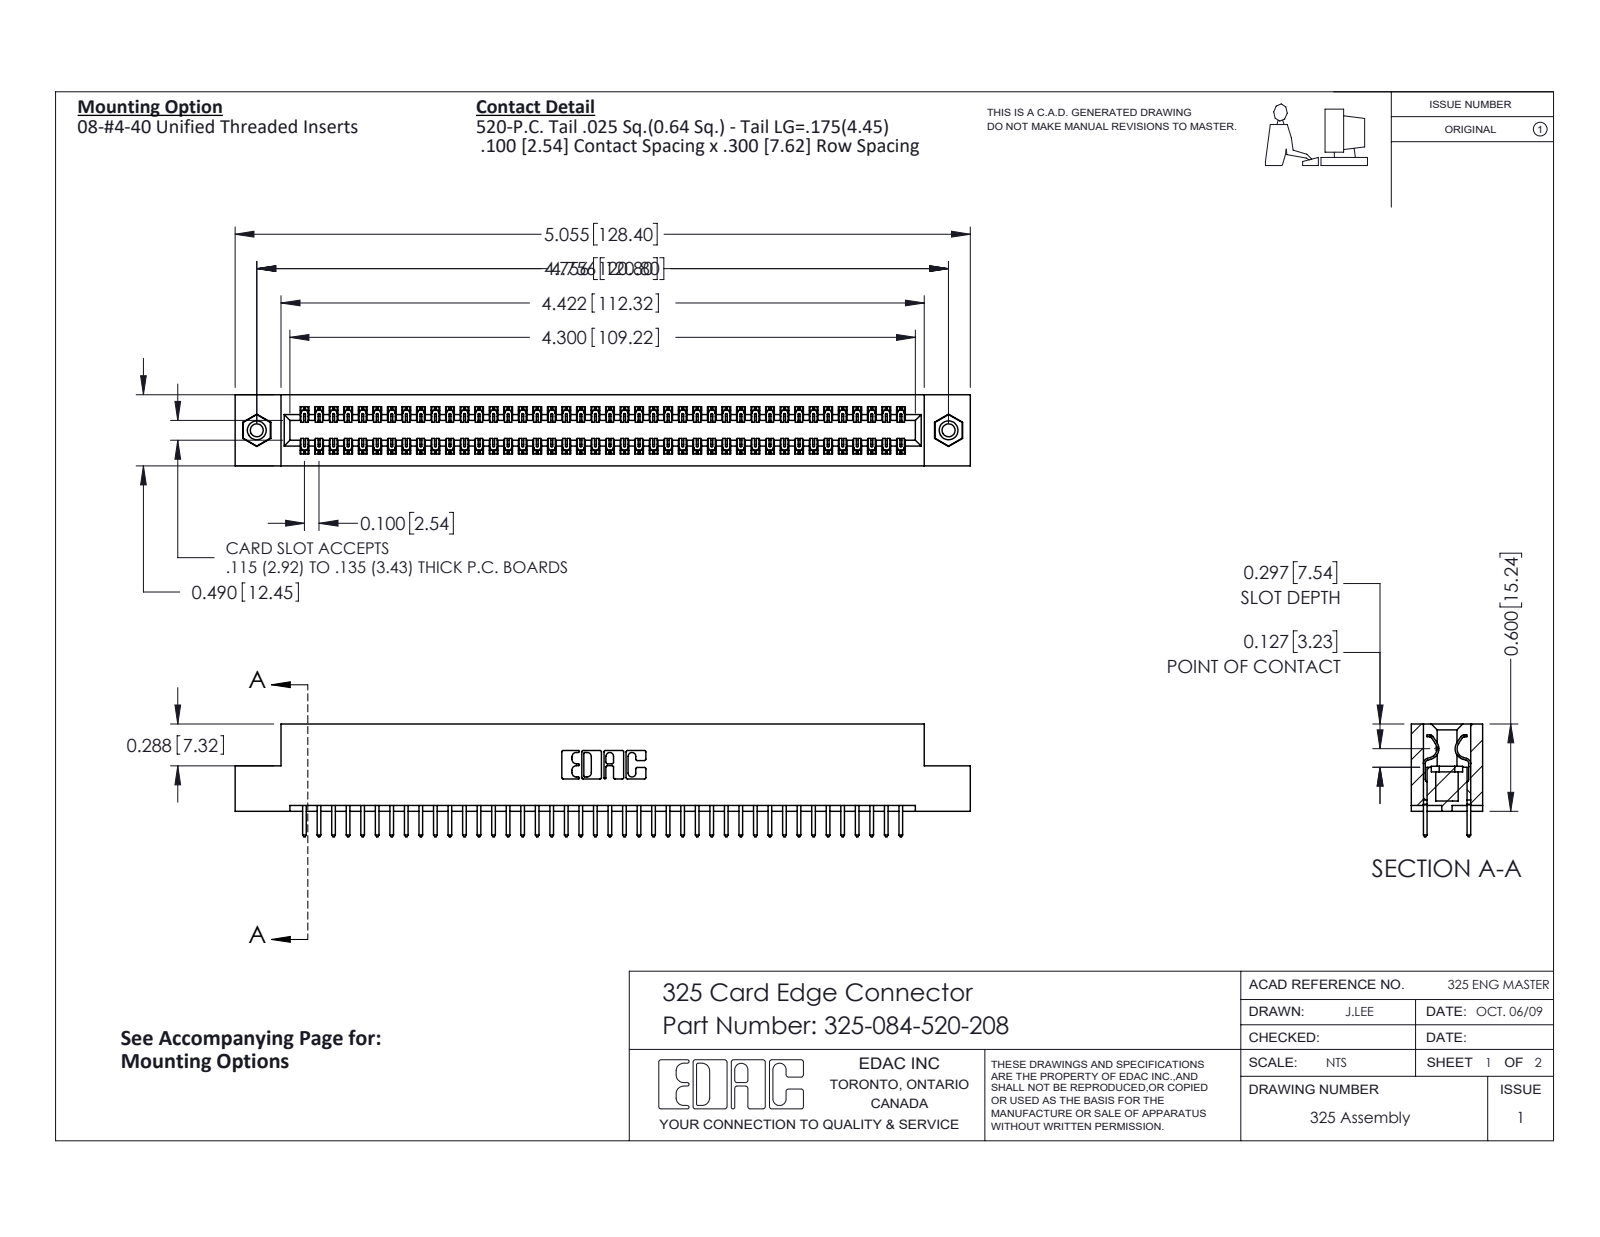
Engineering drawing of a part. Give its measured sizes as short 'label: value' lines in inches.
name: 325-292-001_325-293-120; 325 Part_TI; 345-250-001_345-250-003-102; 325-084-520-208
written by: SolidWorks 2016 (CONFIG_CONTROL_DESIGN)
unit: in
bodies: 87 solids, 4542 faces (3126 planar, 1400 cylindrical, 16 other)
size: 5.055 × 0.775 × 0.49
volume: 1.01 in³; area: 30.82 in²
holes: 2× ⌀0.089, 2× ⌀0.125, 2× ⌀0.16
bosses: 2× ⌀0.155
rounds: 126× R0.006, 84× R0.01, 22× R0.01, 6× R0.007, 6× R0.031, 3× R0.026, 2× R0.014, 2× R0.022
face distances: 0.083, 0.407, 0.3, 0.49, 0.107, 0.383, 0.025, 0.325, 0.275, 0.56
hole spacings: 4.756
